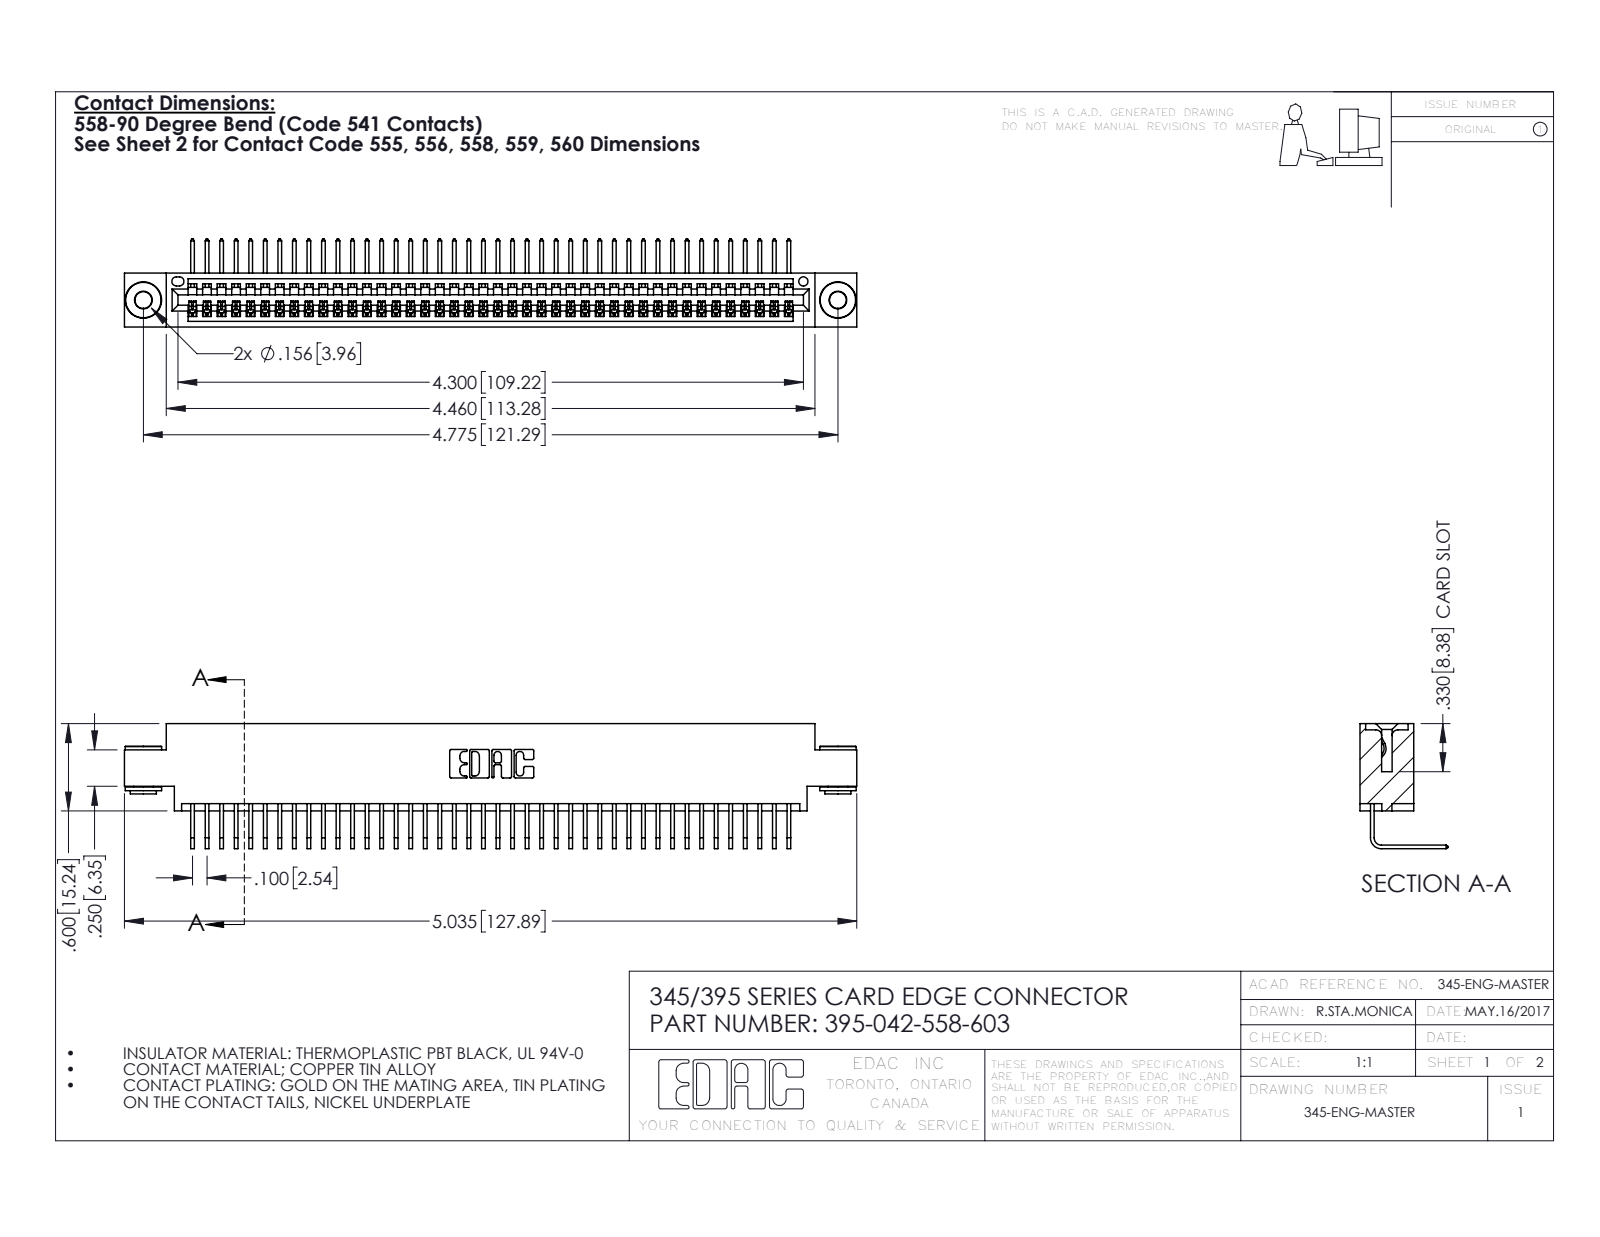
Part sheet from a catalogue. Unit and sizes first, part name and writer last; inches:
Units: inches
Overall size (bounding box): 5.035 × 0.859 × 0.605
Round holes (diameter × count): ⌀0.116 ×2, ⌀0.156 ×2, ⌀0.064 ×1
Round bosses / shafts (diameter × count): ⌀0.25 ×2, ⌀0.18 ×2, ⌀0.136 ×2
Partial cylindrical surfaces — rounded edges, fillets, slot ends (radius × count): R0.006 ×84, R0.01 ×22, R0.007 ×6, R0.031 ×6, R0.026 ×3, R0.031 ×2, R0.04 ×2, R0.014 ×1
Main face-to-face distances: 0.072, 0.298, 0.37, 0.2, 0.098, 0.272, 0.025, 0.225, 0.175, 0.149
Hole centre spacings: 0.27, 4.539, 4.775
Volume: 0.744 in³ · Surface area: 26.92 in²
Bodies: 45 solids, 2688 faces (1858 planar, 822 cylindrical, 8 other)
Part name (STEP PRODUCT): 345 Part_0.170 Offset - 0.156 Dia-TH; 395-042-558-603; 345-292-001_558 Tail - 2; 345-250-002_345-250-002-102
STEP written by: SolidWorks 2016 (CONFIG_CONTROL_DESIGN)
